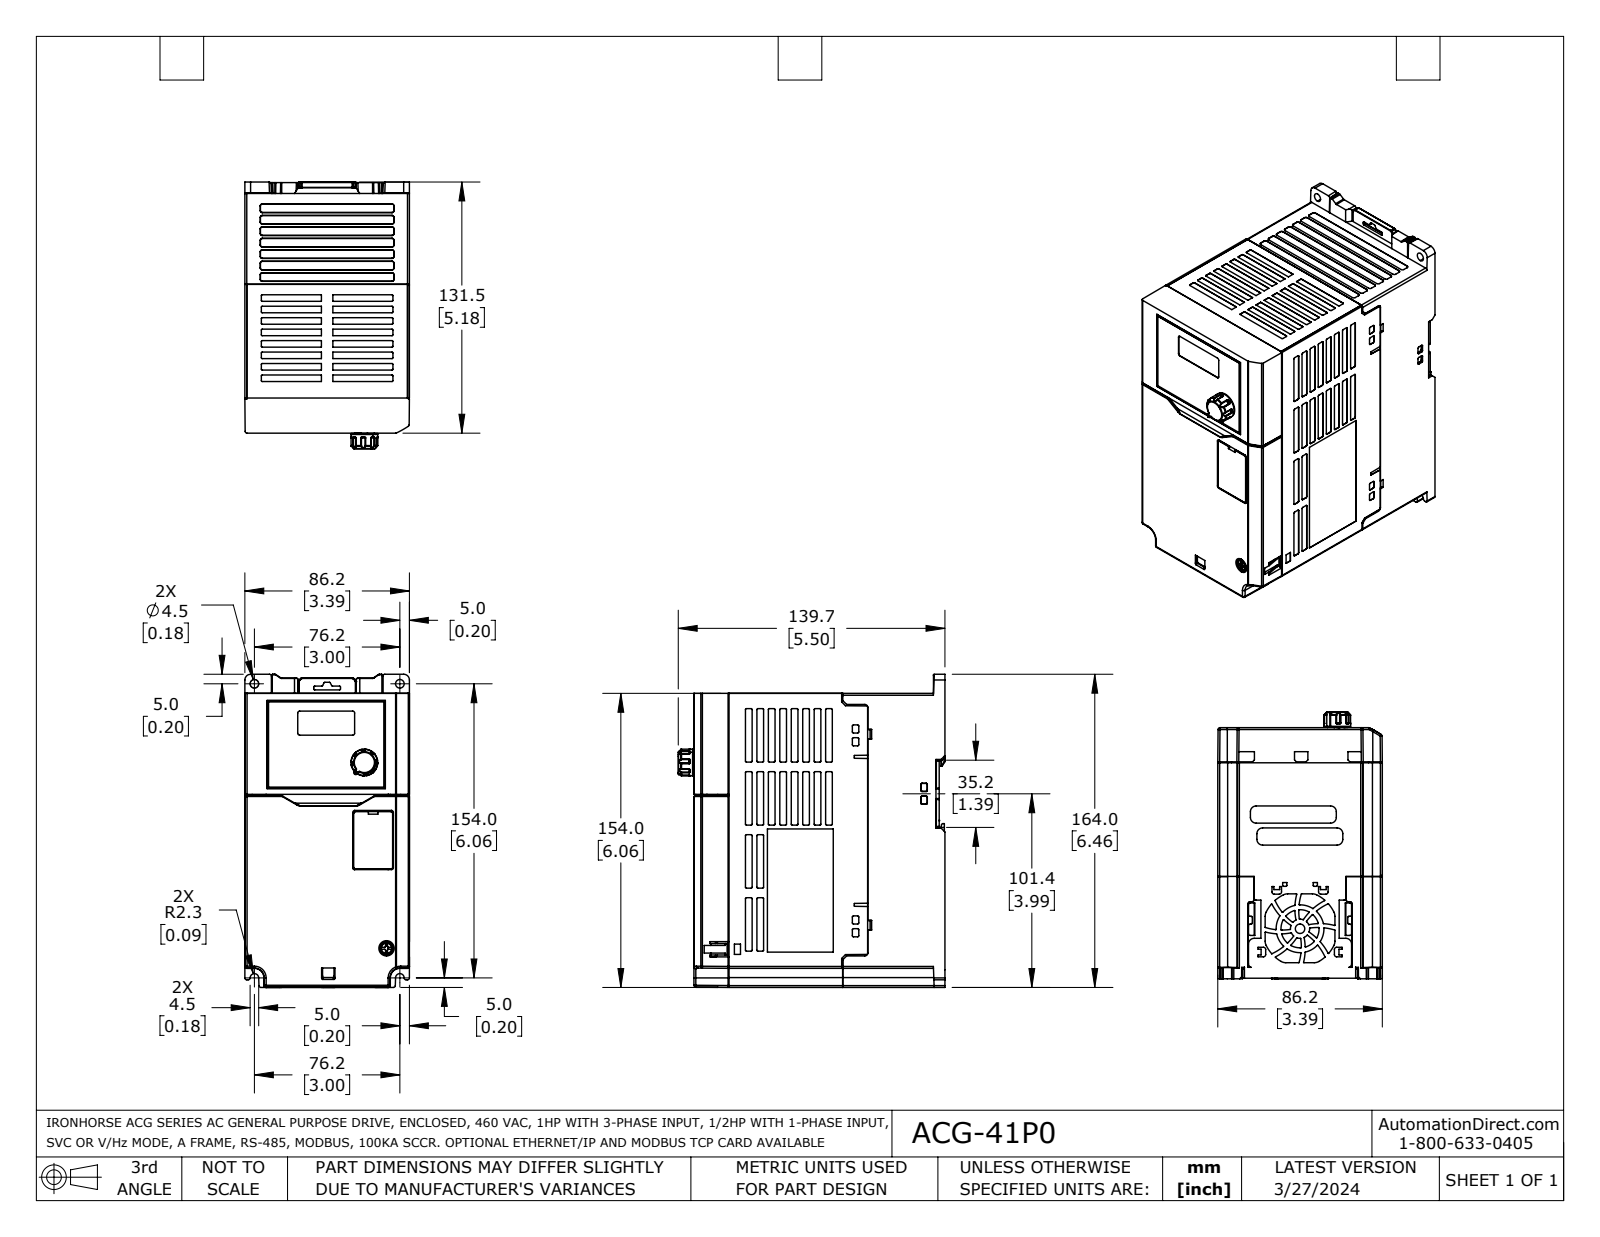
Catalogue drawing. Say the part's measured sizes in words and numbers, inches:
The part is named "ACG-41P0". Its 3-D file was written by "SolidWorks 2021 (AUTOMOTIVE_DESIGN)". It is 6 solids with 4492 faces: 1868 planar, 1308 cylindrical and 1316 other. Overall it measures 6.457 by 5.5 by 3.394 inches. Its volume is 101.9 cubic inches and its surface area 197.5 square inches. Round holes: 1 of diameter 0.039, 1 of diameter 0.276, 1 of diameter 0.472. Round bosses or shafts: 1 of diameter 0.551, 1 of diameter 0.543, 1 of diameter 0.236. Partial cylindrical surfaces (rounded edges, fillets, slot ends): 343 of radius 0.008, 288 of radius 0.02, 85 of radius 0.039, 46 of radius 0.018, 27 of radius 0.012, 17 of radius 0.031, 16 of radius 0.023, 12 of radius 0.118. The main face-to-face distances are 3.394, 5.059, 3.392, 5.047, 6.063, 6.061, 5.165, 0.106, 3.39, 6.061. The hole center spacings are 0.276, 3.675, 3.858.
